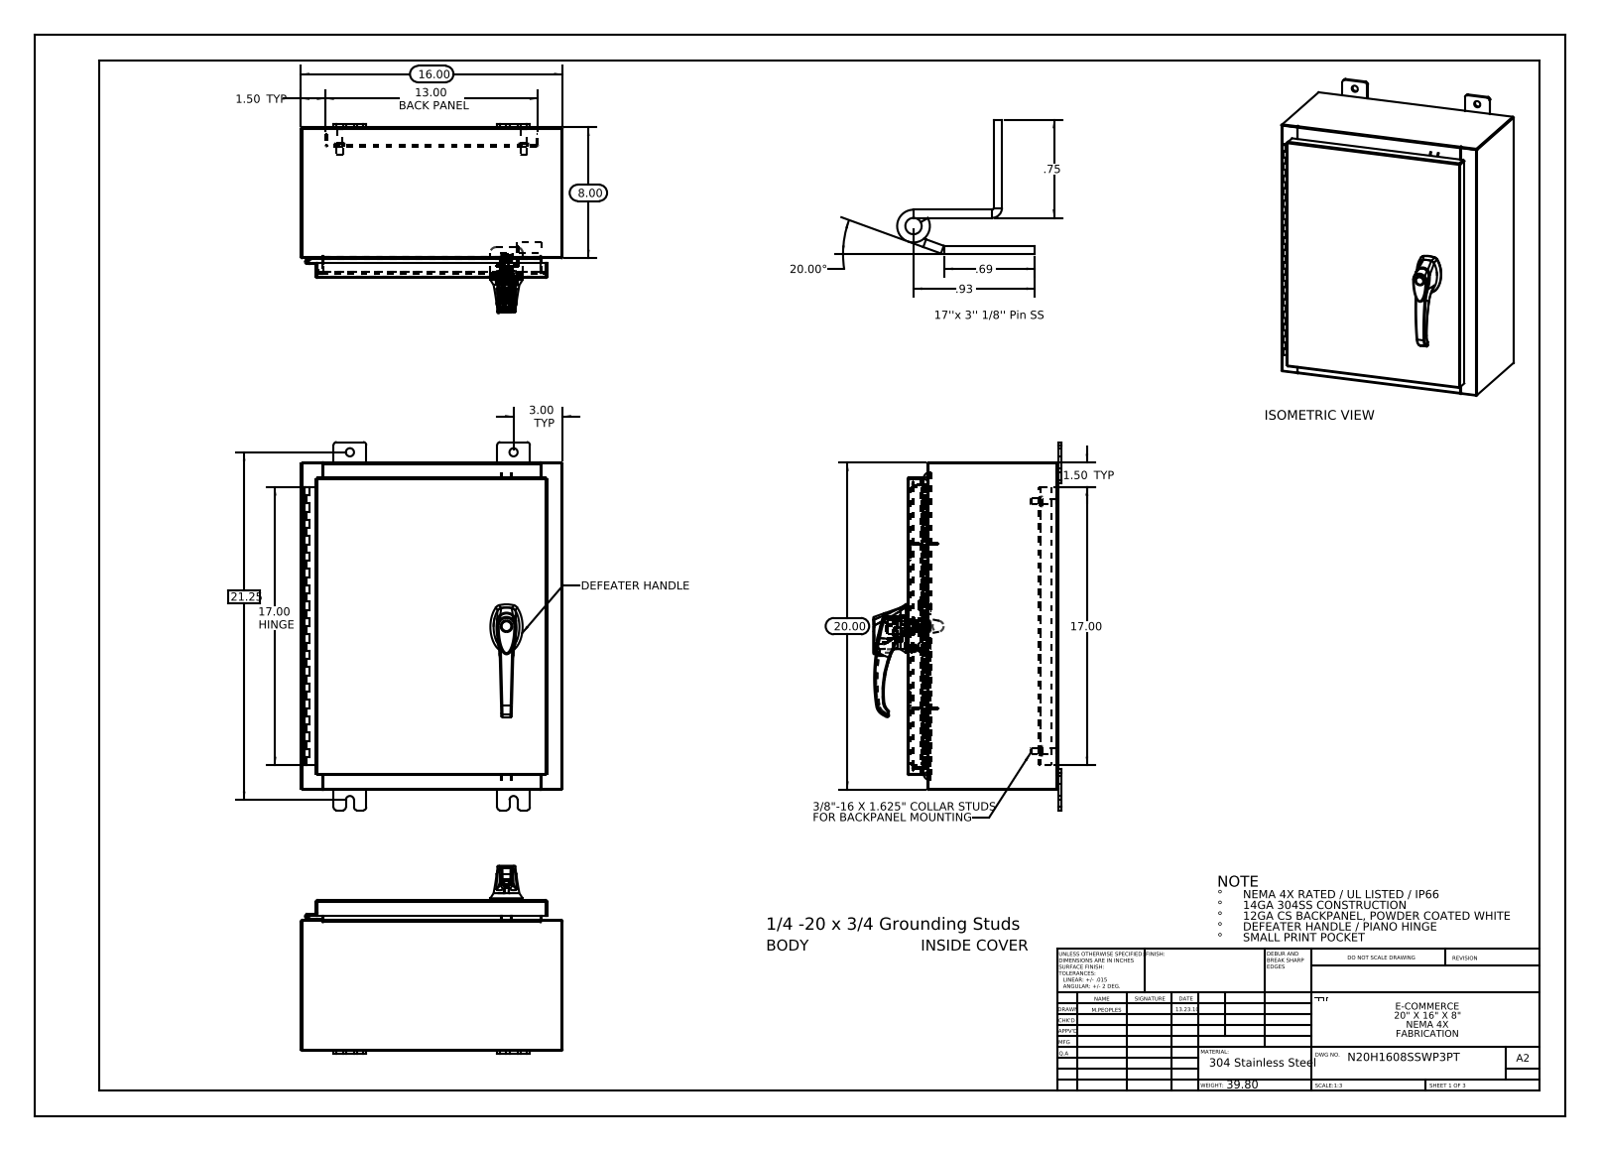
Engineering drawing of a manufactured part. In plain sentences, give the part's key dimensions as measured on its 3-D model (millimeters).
The part is named "00005090; N20H1608SSWP3PT 125 Pin Hinge; 2616310101; N20H1608SSWP3PT Defeater Handle Rod (+8 more)". Its 3-D file was written by "SolidWorks 2013 (CONFIG_CONTROL_DESIGN)". It is 31 solids with 2316 faces: 817 planar, 845 cylindrical and 654 other. Overall it measures 571.5 by 406.4 by 292 millimeters. Its volume is 2 334 000 cubic millimeters and its surface area 2 269 000 square millimeters. Round holes: 8 of diameter 12.7, 4 of diameter 6.4, 3 of diameter 3.5, 3 of diameter 4.1, 2 of diameter 2, 2 of diameter 5.2, 2 of diameter 8, 2 of diameter 11.1, 1 of diameter 3.2, 1 of diameter 3.2, 1 of diameter 5, 1 of diameter 7. Round bosses or shafts: 4 of diameter 15.9, 4 of diameter 9.5, 4 of diameter 8.4, 1 of diameter 30, 1 of diameter 19, 1 of diameter 17.3, 1 of diameter 16.8, 1 of diameter 16.2. Partial cylindrical surfaces (rounded edges, fillets, slot ends): 37 of radius 3, 33 of radius 0.2, 24 of radius 4.8, 22 of radius 0.3, 18 of radius 2.2, 15 of radius 1, 12 of radius 0.7, 6 of radius 0.2. The main face-to-face distances are 1.9, 231.8, 404.5, 229.9, 233.7, 506.1, 2.6, 25.4, 27.3, 204.5. The hole center spacings are 86.5, 304.2, 7.5, 15.9, 21.4, 31.8, 33.4, 39.6.
